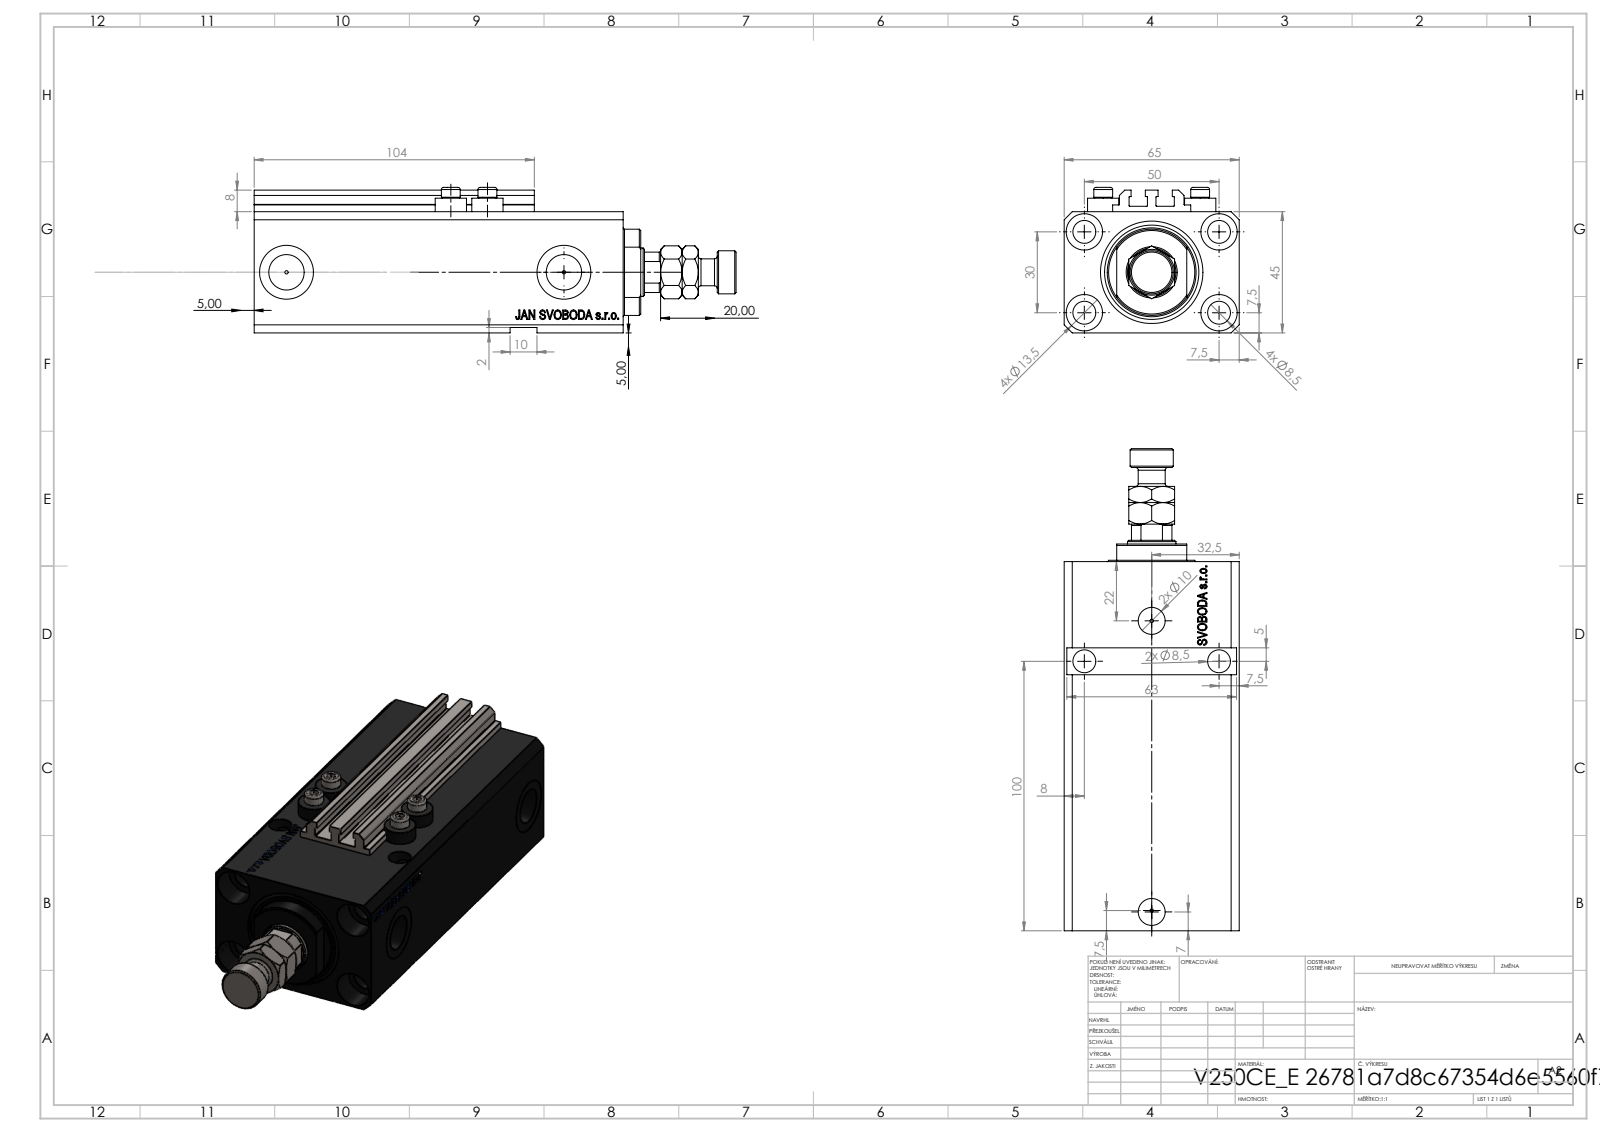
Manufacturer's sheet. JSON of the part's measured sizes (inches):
{"part_name": "V250CE_C_VCP; ALLEN BOLT V250CE; V250CE_E_Body; MFA (+1 more)", "step_written_by": "SolidWorks 2019 (CONFIG_CONTROL_DESIGN)", "units": "inches", "bodies": {"solids": 9, "faces": 1155, "planar": 531, "cylindrical": 162, "other": 462}, "overall_size": [7.047, 2.559, 2.126], "volume_in3": 21.5, "surface_area_in2": 150, "round_holes": [[0.335, 9], [0.049, 4], [0.157, 4], [0.531, 4], [0.394, 2], [0.518, 2], [0.787, 2], [0.709, 1], [0.984, 1], [1.496, 1]], "round_bosses_or_shafts": [[0.457, 4], [0.276, 4], [0.63, 1], [0.394, 1]], "partial_cylinders_radius": [[0.008, 10], [0.335, 1], [0.63, 1]], "face_to_face_distances": [1.772, 2.559, 1.85, 0.551, 0.079, 4.843, 0.098, 0.394, 0.945, 0.803], "hole_center_spacings": [1.148, 1.969, 0.535, 0.595, 1.098, 1.181, 1.323, 1.324]}
